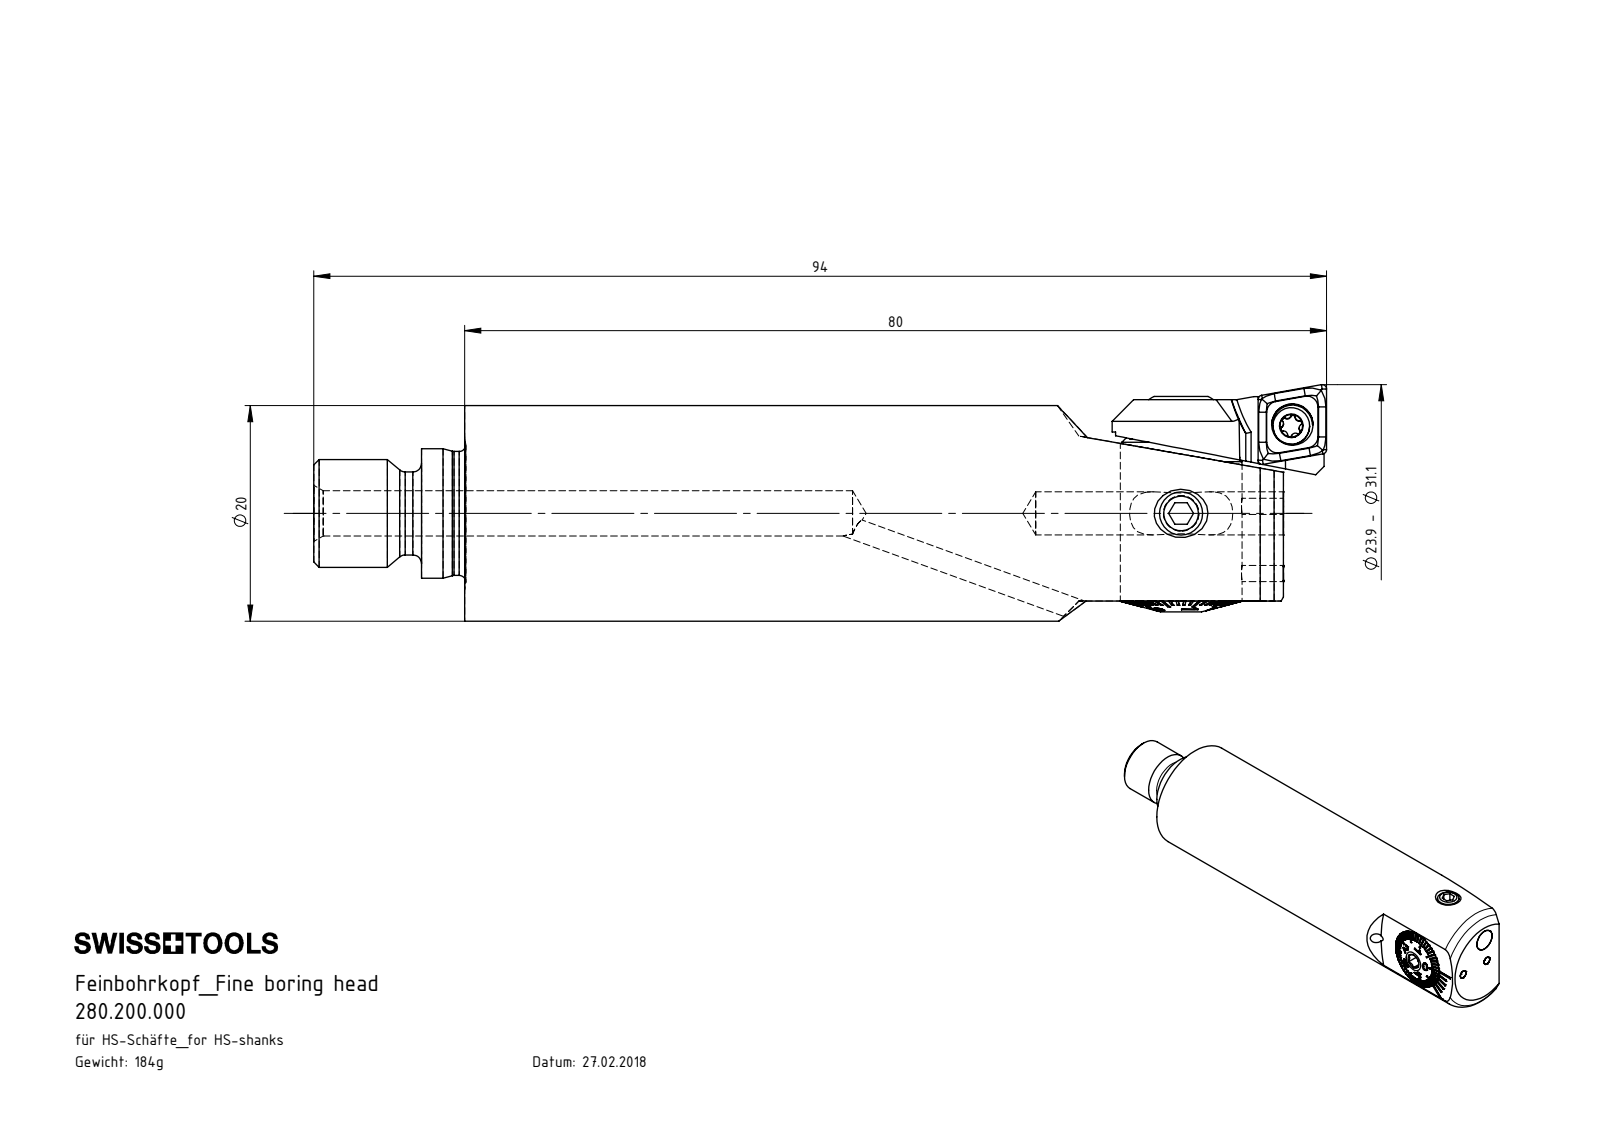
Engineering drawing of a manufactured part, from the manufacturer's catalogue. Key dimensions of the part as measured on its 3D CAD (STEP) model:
Part name (STEP PRODUCT): F20-BG2.001.000_B; F20-BG4.001.000_mit Aufsatz; 280.200.000; HP1-F20.K10.080_A (+7 more)
STEP written by: SolidWorks 2017 (CONFIG_CONTROL_DESIGN)
Units: millimetres
Bodies: 11 solids, 598 faces (281 planar, 96 cylindrical, 221 other)
Overall size (bounding box): 90 × 20 × 20
Volume: 22 759 mm³ · Surface area: 9 157 mm²
Round holes (diameter × count): ⌀1.4 ×2, ⌀3.3 ×2, ⌀0.5 ×1, ⌀1.5 ×1, ⌀2 ×1, ⌀3.75 ×1, ⌀4 ×1, ⌀4.2 ×1, ⌀4.5 ×1, ⌀5 ×1, ⌀6.6 ×1, ⌀7.05 ×1
Round bosses / shafts (diameter × count): ⌀1.5 ×3, ⌀4 ×2, ⌀20 ×1, ⌀12 ×1, ⌀11.5 ×1, ⌀11.3 ×1, ⌀11 ×1, ⌀10 ×1
Partial cylindrical surfaces — rounded edges, fillets, slot ends (radius × count): R0.3 ×2, R1 ×2, R3.77 ×1
Main face-to-face distances: 76, 3.88, 1, 3.08, 0.8, 3.6, 11.15, 14.23, 15.03, 11.43
Hole centre spacings: 0.75, 5, 5.58, 7.49
